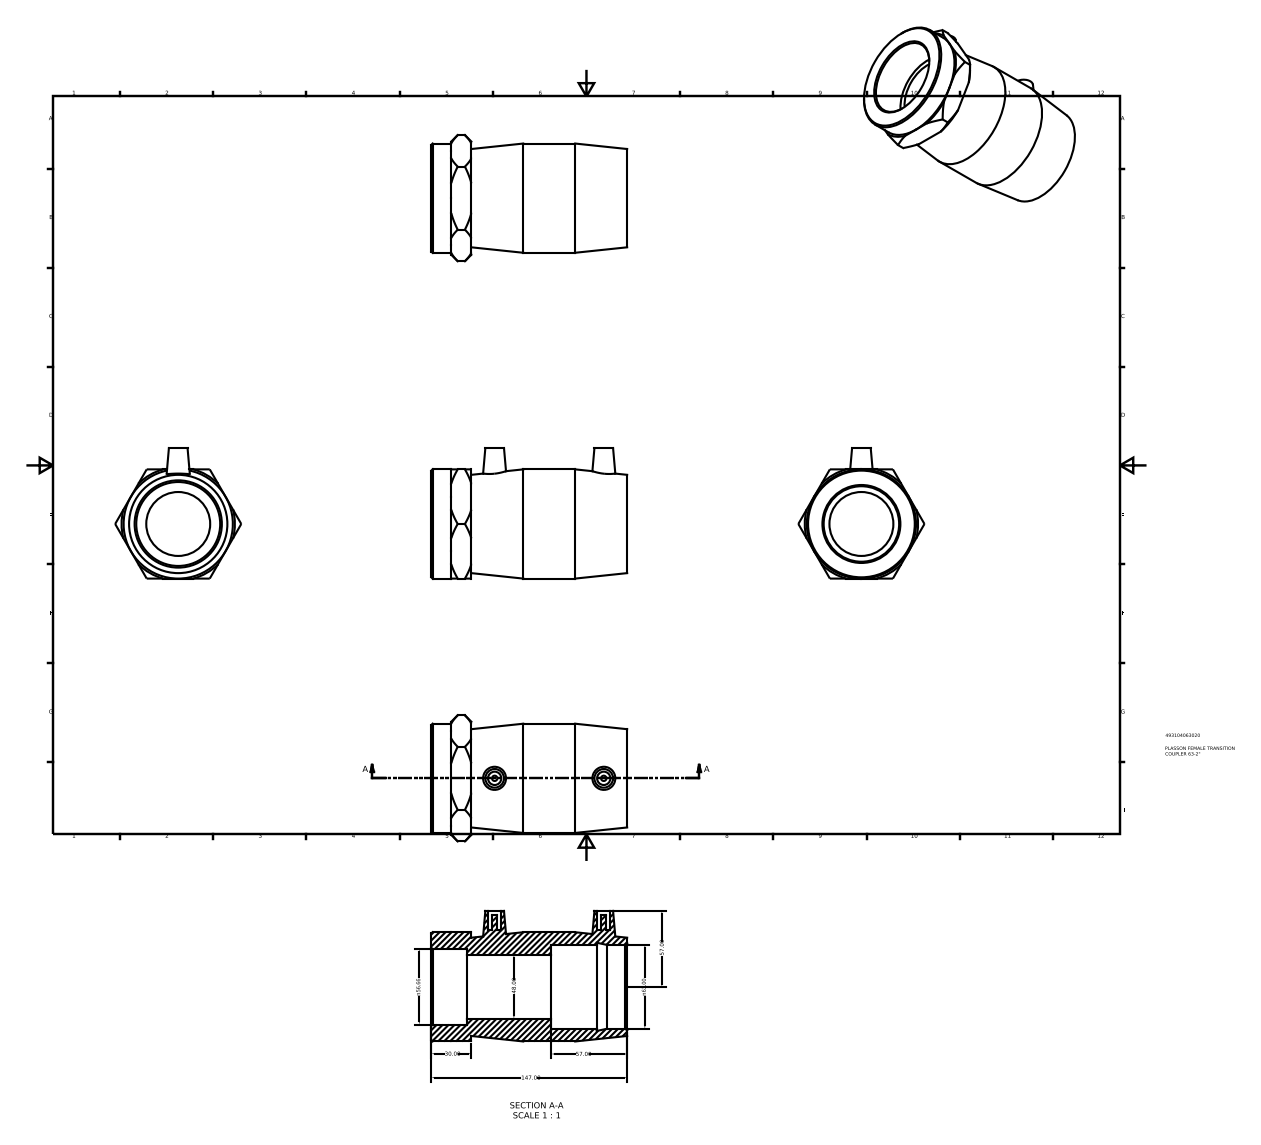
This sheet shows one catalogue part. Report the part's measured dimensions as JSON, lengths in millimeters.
{"part_name": "493104063020", "step_written_by": "Autodesk Inventor 2015 (AUTOMOTIVE_DESIGN)", "units": "millimeters", "bodies": {"solids": 1, "faces": 54, "planar": 24, "cylindrical": 10, "other": 20}, "overall_size": [147, 98, 94.69], "volume_mm3": 387626, "surface_area_mm2": 73427, "round_holes": [[10, 2], [48, 1], [56.66, 1], [63, 1]], "round_bosses_or_shafts": [[4, 2], [82, 1]], "face_to_face_distances": [82, 90, 30, 60, 147, 117, 57, 3, 27, 63], "hole_center_spacings": [81.9]}
